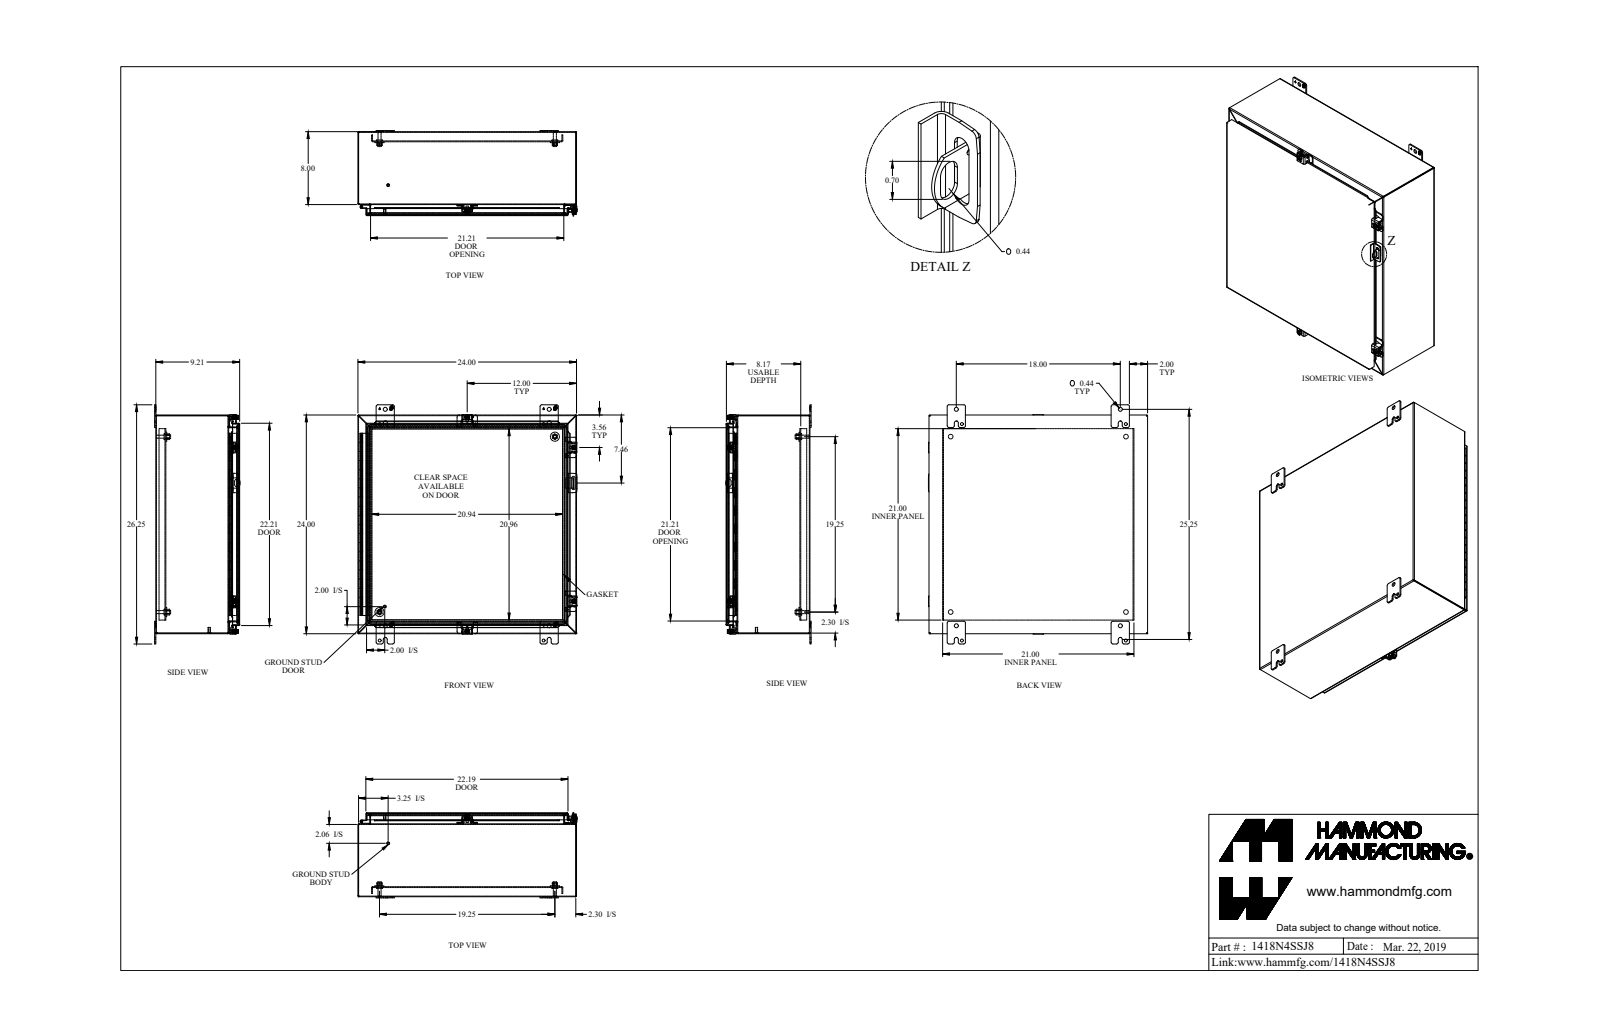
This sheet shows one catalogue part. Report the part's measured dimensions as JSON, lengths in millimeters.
{"part_name": "1418N4SSJ8_Default", "step_written_by": "SolidWorks 2019 (CONFIG_CONTROL_DESIGN)", "units": "millimeters", "bodies": {"solids": 39, "faces": 1499, "planar": 925, "cylindrical": 481, "other": 93}, "overall_size": [666.8, 611.2, 238.1], "volume_mm3": 3495000, "surface_area_mm2": 3618000, "round_holes": [[5.4, 4], [6.7, 4], [8, 4], [9.5, 4], [11.1, 4], [12.7, 4], [7.8, 2], [11.3, 2], [3.2, 1], [4.7, 1]], "round_bosses_or_shafts": [[16.5, 4], [12.7, 4], [9.9, 4], [9.5, 4], [8.4, 4], [6.2, 4], [25.4, 2], [8, 2]], "partial_cylinders_radius": [[4.8, 26], [0.9, 24], [2.7, 24], [1.2, 21], [3.6, 21], [6.4, 20], [3.2, 10], [1.1, 8]], "face_to_face_distances": [1.8, 607.8, 1.8, 230.3, 232.1, 232.1, 233.9, 2.4, 23.8, 25.6], "hole_center_spacings": [489, 250.4, 457.2, 595.4, 691.5, 710.8, 44.1, 474.6]}
